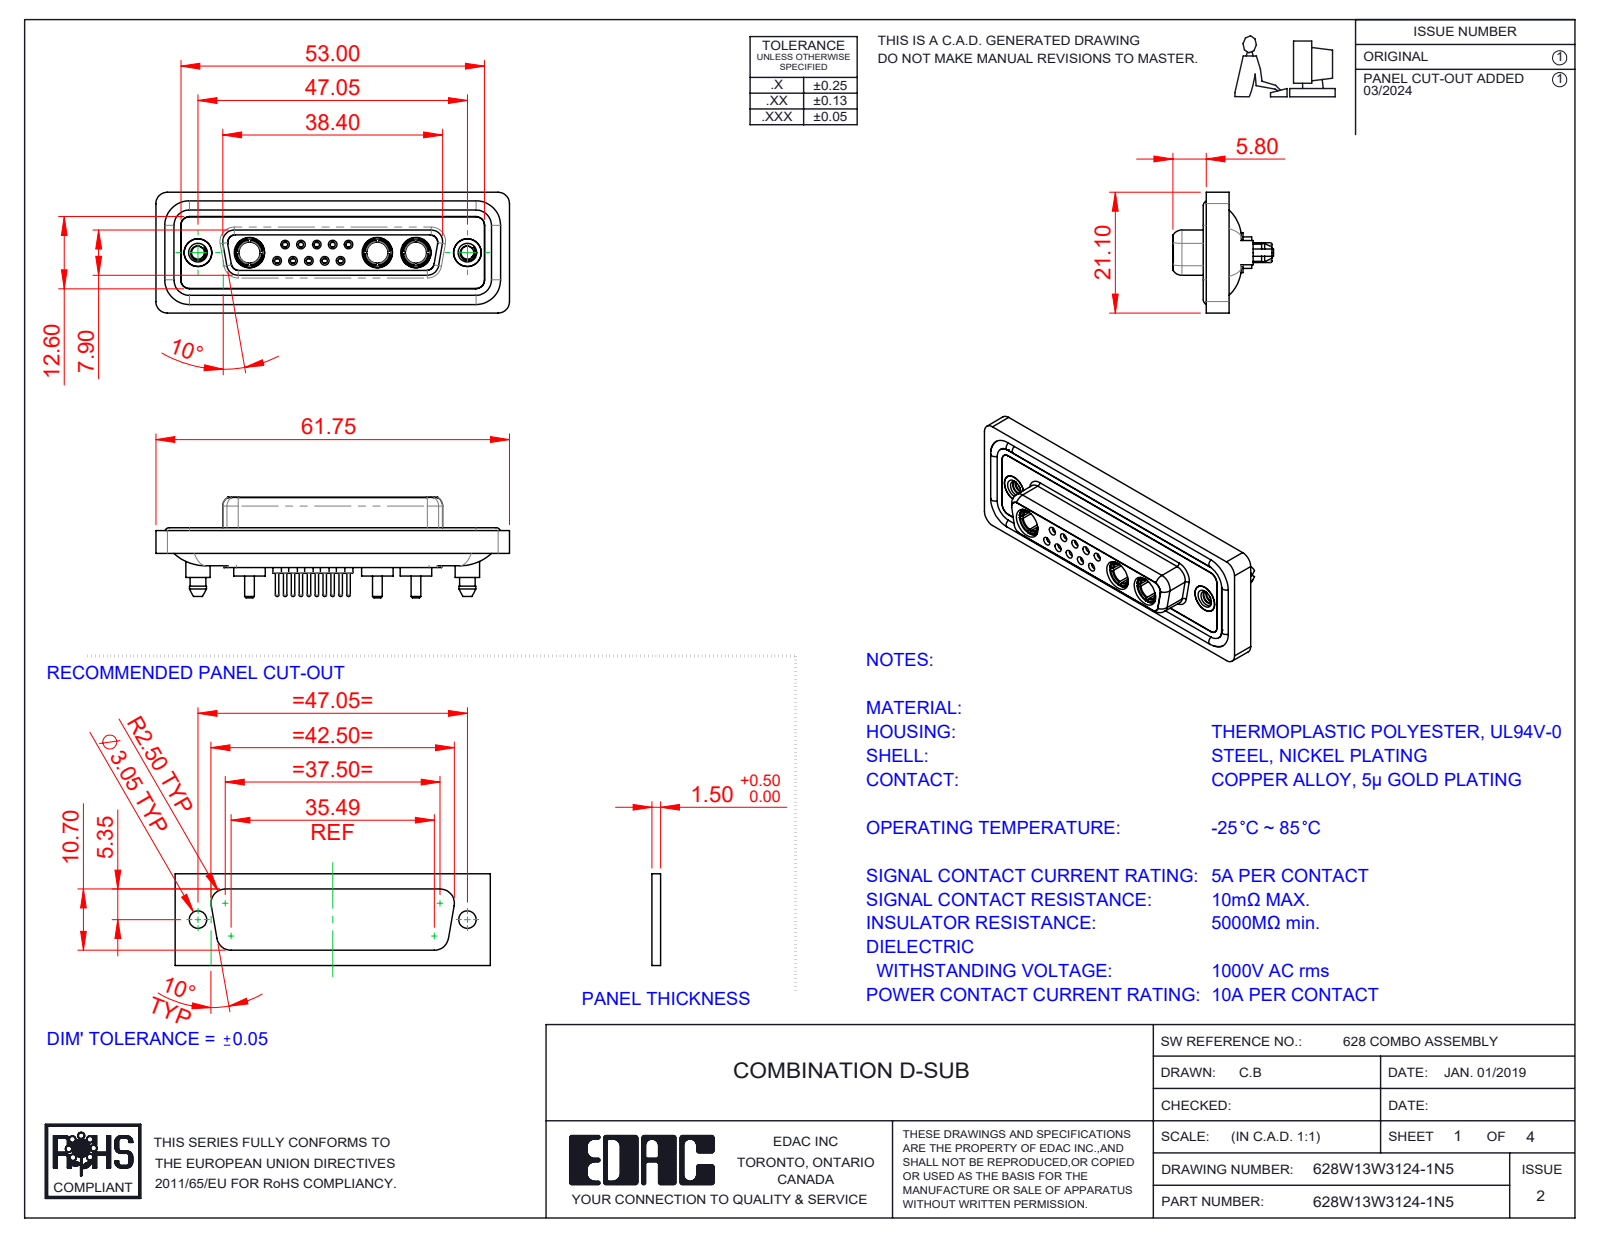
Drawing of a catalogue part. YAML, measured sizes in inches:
part_name: "628Combo Shell Rear_25 Contacts; 628Combo Contact Row 1_24; 628Combo Housing_13W3; 628Combo Waterproof Housing_25 Contacts (+5 more)"
step_written_by: "SolidWorks 2023 (CONFIG_CONTROL_DESIGN)"
units: inches
bodies: {solids: 23, faces: 1208, planar: 358, cylindrical: 479, other: 371}
overall_size: [2.431, 0.831, 0.691]
volume: 0.51
surface_area: 21.71
round_holes:
  - {diameter: 0.035, count: 10}
  - {diameter: 0.043, count: 10}
  - {diameter: 0.059, count: 10}
  - {diameter: 0.079, count: 10}
  - {diameter: 0.063, count: 5}
  - {diameter: 0.067, count: 5}
  - {diameter: 0.191, count: 5}
  - {diameter: 0.146, count: 3}
  - {diameter: 0.209, count: 3}
  - {diameter: 0.089, count: 2}
  - {diameter: 0.157, count: 2}
  - {diameter: 0.159, count: 2}
round_bosses_or_shafts:
  - {diameter: 0.087, count: 10}
  - {diameter: 0.024, count: 10}
  - {diameter: 0.063, count: 9}
  - {diameter: 0.217, count: 3}
  - {diameter: 0.205, count: 3}
  - {diameter: 0.195, count: 3}
  - {diameter: 0.187, count: 3}
  - {diameter: 0.148, count: 3}
partial_cylinders:
  - {radius: 0.059, count: 24}
  - {radius: 0.079, count: 18}
  - {radius: 0.063, count: 10}
  - {radius: 0.053, count: 8}
  - {radius: 0.01, count: 4}
  - {radius: 0.02, count: 4}
  - {radius: 0.024, count: 4}
  - {radius: 0.026, count: 4}
face_to_face_distances: [0.016, 0.071, 0.293, 0.222, 0.02, 0.26, 0.278, 0.063, 0.114, 0.043]
hole_center_spacings: [0.124, 0.109, 0.198, 0.198, 0.218, 0.327, 0.295, 0.109]
